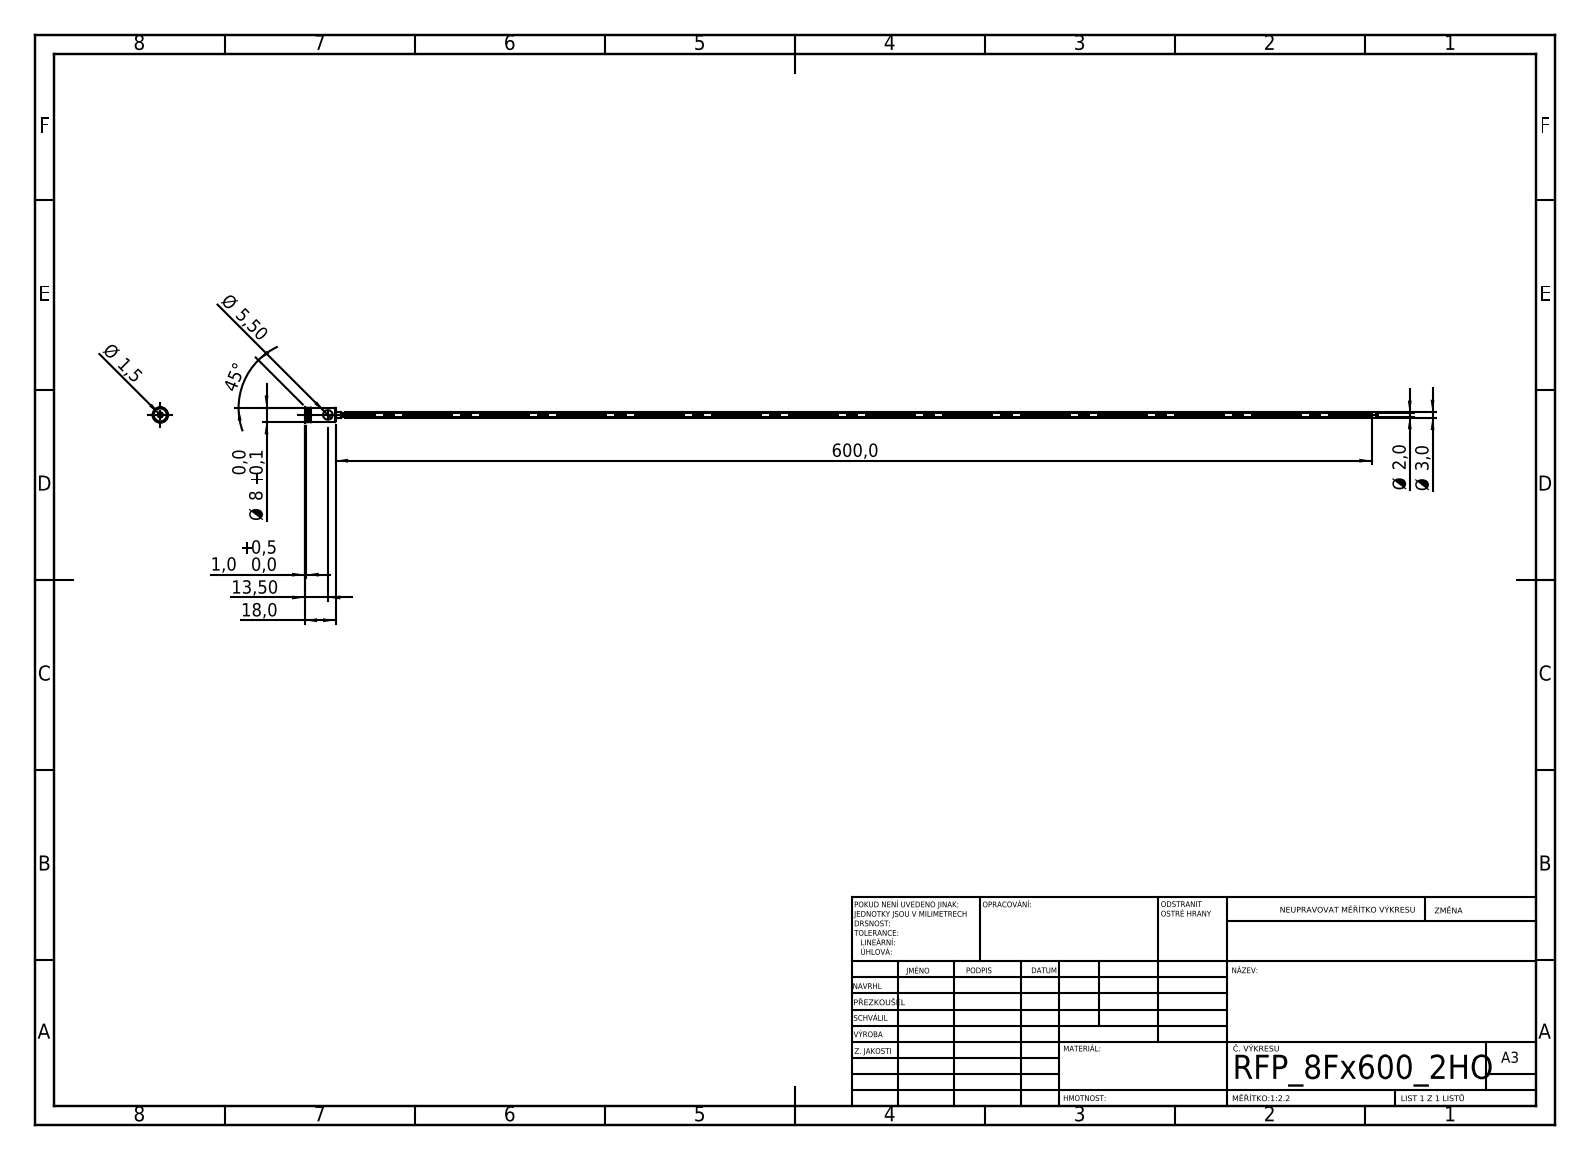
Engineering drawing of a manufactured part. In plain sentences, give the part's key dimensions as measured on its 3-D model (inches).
Its 3-D file was written by "SolidWorks 2019 (CONFIG_CONTROL_DESIGN)". It is 1 solid with 44 faces: 20 planar, 16 cylindrical and 8 other. Overall it measures 24.331 by 0.354 by 0.354 inches. Its volume is 0.095 cubic inches and its surface area 11.31 square inches. Round holes: 1 of diameter 0.059, 1 of diameter 0.217. Round bosses or shafts: 1 of diameter 0.354, 1 of diameter 0.315, 1 of diameter 0.118, 1 of diameter 0.079. The main face-to-face distances are 0.709, 0.134, 0.63, 0.079, 0.618, 0.091, 0.118, 0.736, 0.748, 0.827.
